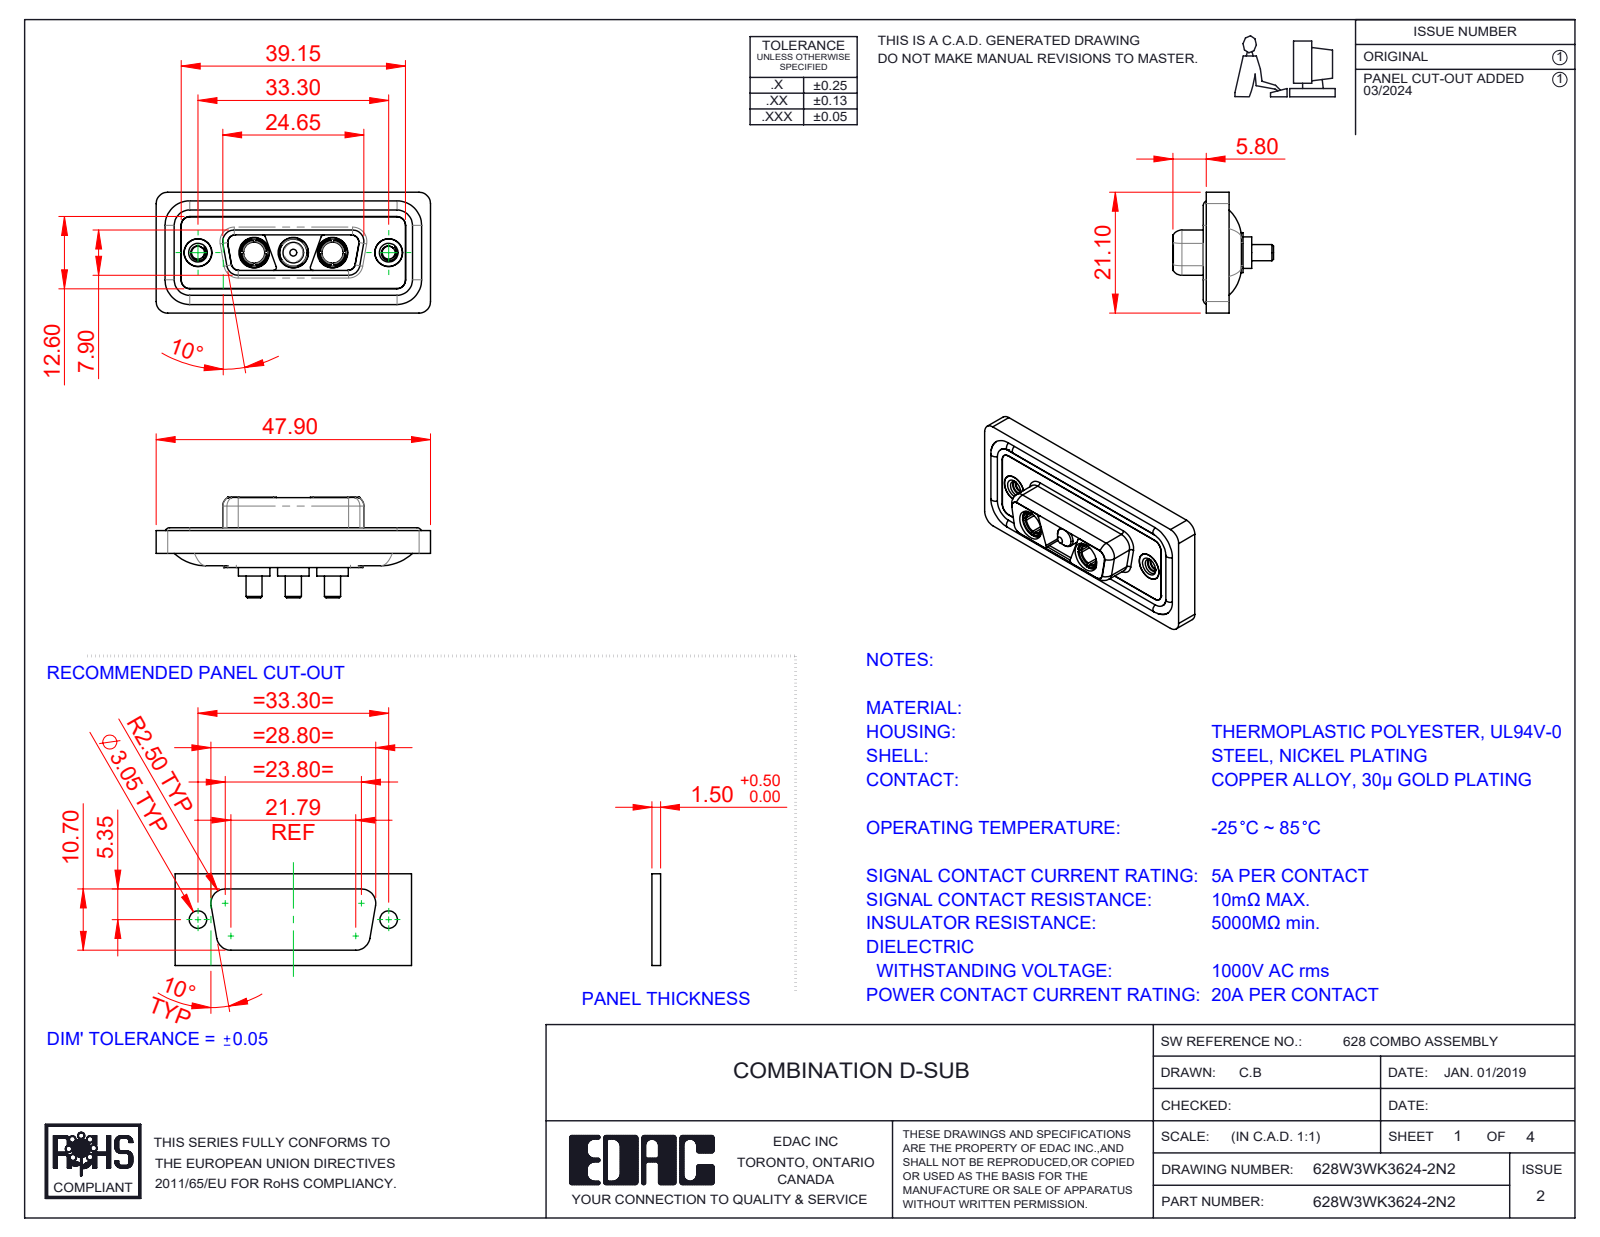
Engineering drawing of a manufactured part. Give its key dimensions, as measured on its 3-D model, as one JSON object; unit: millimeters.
{"part_name": "628W3WK3624-2N2; 628Combo Shell Rear_15 Contacts; 628Combo Waterproof Housing_15 Contacts; 628Combo Threaded Rivet_2 (+4 more)", "step_written_by": "SolidWorks 2023 (CONFIG_CONTROL_DESIGN)", "units": "millimeters", "bodies": {"solids": 13, "faces": 583, "planar": 178, "cylindrical": 258, "other": 147}, "overall_size": [47.9, 21.1, 17.55], "volume_mm3": 5878, "surface_area_mm2": 9505, "round_holes": [[4.85, 5], [5.3, 3], [2.26, 2], [3.7, 2], [4, 2], [4.05, 2], [5, 2]], "round_bosses_or_shafts": [[1.6, 4], [5.5, 3], [5.2, 3], [4.75, 3], [3.75, 3], [2.8, 3], [4.96, 2], [4.95, 2]], "partial_cylinders_radius": [[1.5, 22], [2, 20], [1.35, 12], [0.5, 8], [1.6, 8], [0.25, 4], [0.6, 4], [0.65, 4]], "face_to_face_distances": [0.4, 1.6, 1.8, 0.5, 1.1, 2.9, 5.65, 7.05, 1.5, 5.35], "hole_center_spacings": [6.85, 9.8, 16.65, 23.5, 13.7, 33.3]}
